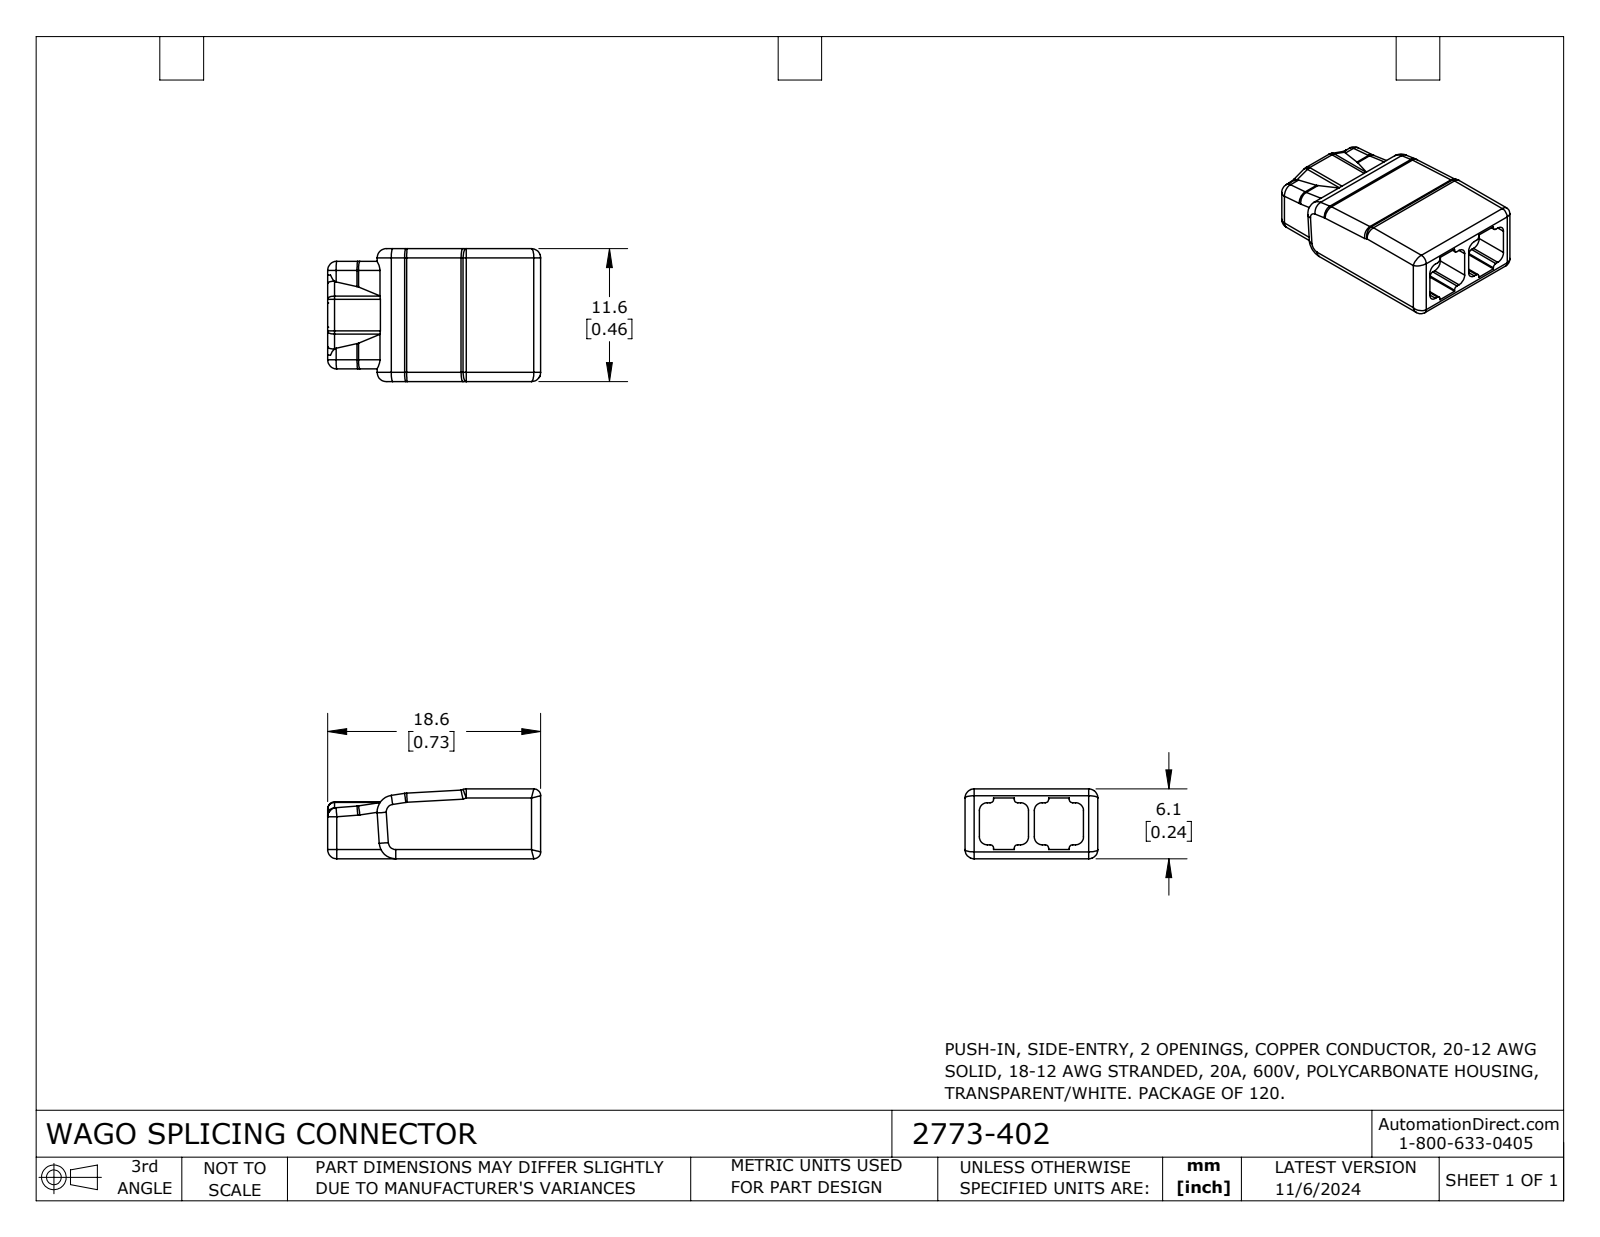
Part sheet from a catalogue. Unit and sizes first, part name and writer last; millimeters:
Units: millimetres
Overall size (bounding box): 18.6 × 11.6 × 6.1
Partial cylindrical surfaces — rounded edges, fillets, slot ends (radius × count): R0.8 ×27, R0.3 ×8, R0.7 ×8, R0.6 ×5, R1.45 ×2, R2 ×2
Main face-to-face distances: 6.1, 11.6, 0.8, 1.1, 10.5, 15.6, 1.25, 3, 4.75, 6.85
Volume: 1 033 mm³ · Surface area: 818 mm²
Bodies: 1 solid, 131 faces (54 planar, 55 cylindrical, 22 other)
Part name (STEP PRODUCT): 2773-402
STEP written by: SolidWorks 2023 (CONFIG_CONTROL_DESIGN)
